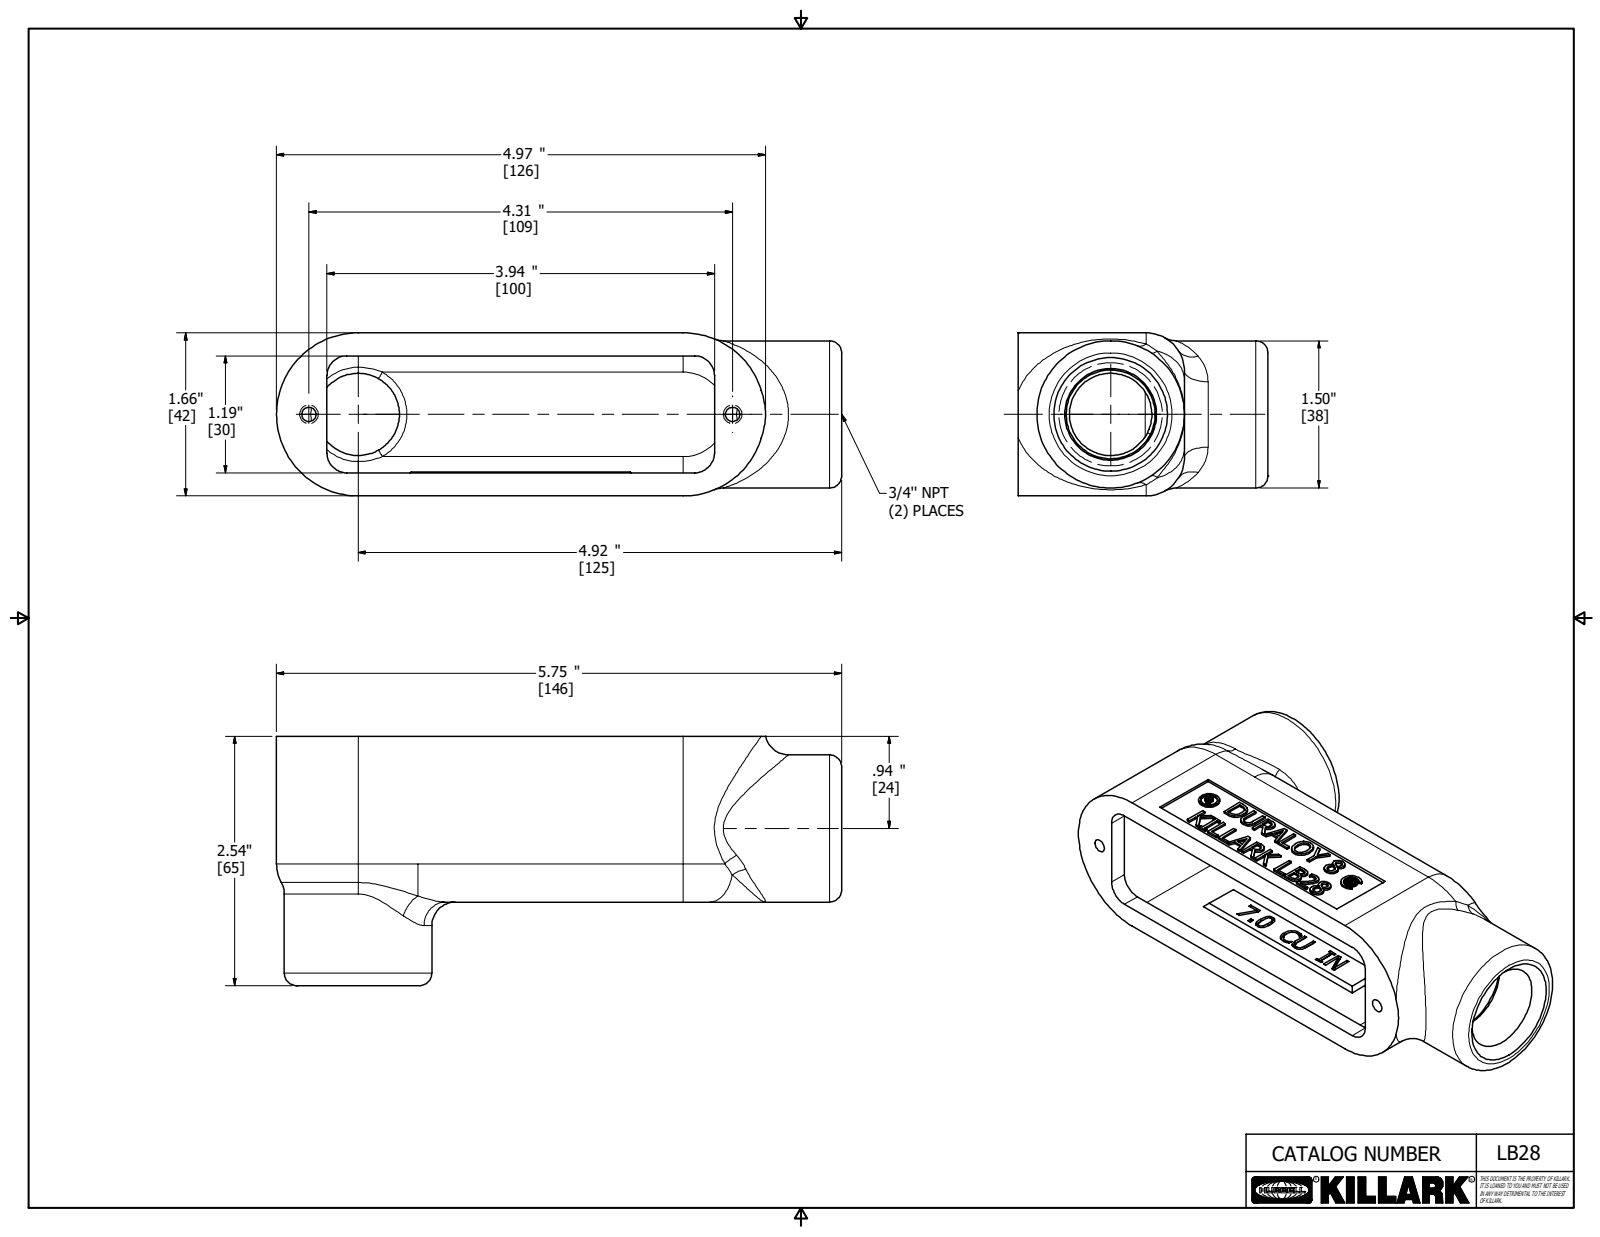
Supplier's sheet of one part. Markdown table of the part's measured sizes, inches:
| quantity | value |
| --- | --- |
| part name | 21715-2 |
| STEP written by | Autodesk Inventor 2018 (AUTOMOTIVE_DESIGN) |
| units | inches |
| bodies | 1 solid, 501 faces (284 planar, 36 cylindrical, 181 other) |
| overall size | 5.748 × 2.54 × 1.66 |
| volume | 6.319 in³ |
| surface area | 62.69 in² |
| round holes (diameter × count) | 0.145 × 2, 1.055 × 2, 0.187 × 1 |
| round bosses / shafts (diameter × count) | 1.5 × 2, 0.23 × 1 |
| partial cylindrical surfaces (radius × count) | 0.2 × 6, 0.39 × 2, 0.63 × 2, 0.83 × 2, 0.007 × 1, 0.029 × 1, 0.052 × 1, 0.074 × 1 |
| main face-to-face distances | 0.2, 1.46, 1.49, 1.26, 1.69, 1.66, 0.03, 1.63, 1.43, 0.17 |
| hole center spacings | 0.501, 3.809, 4.31 |
